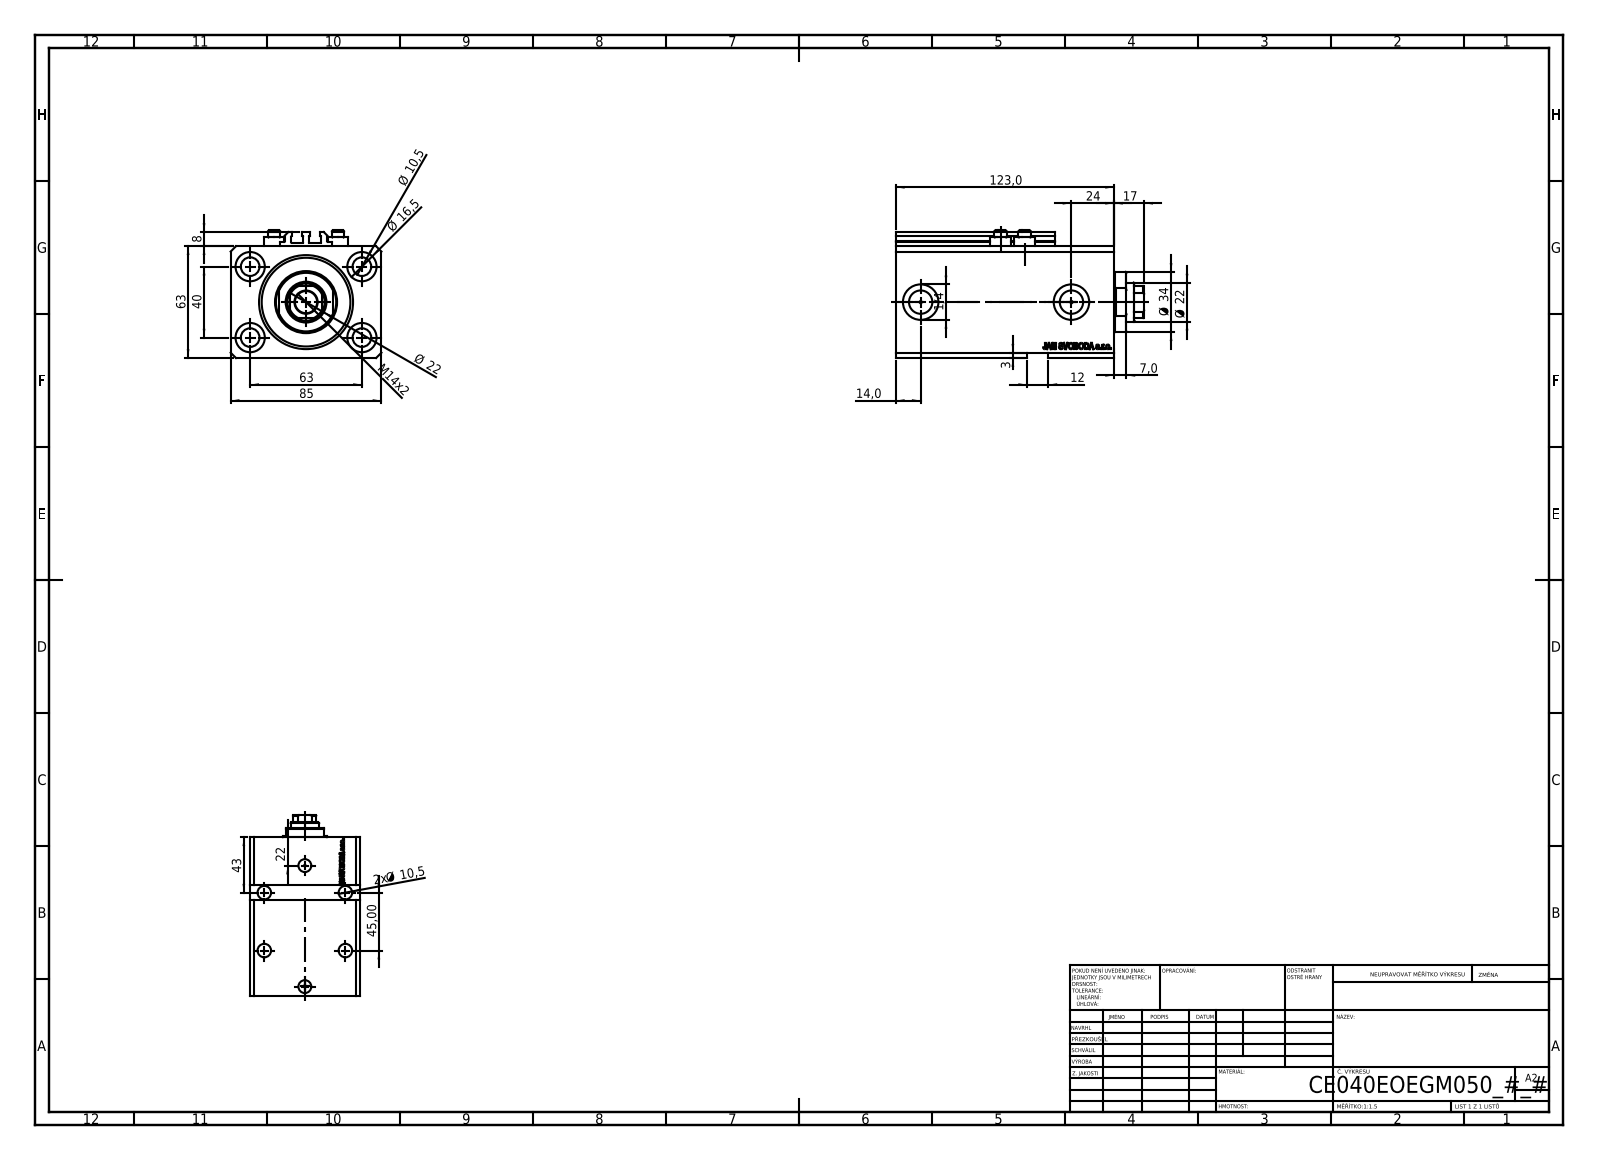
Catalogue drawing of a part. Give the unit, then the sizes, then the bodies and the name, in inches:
Units: inches
Overall size (bounding box): 5.512 × 3.346 × 2.835
Round holes (diameter × count): ⌀0.413 ×8, ⌀0.049 ×4, ⌀0.157 ×4, ⌀0.65 ×4, ⌀0.394 ×2, ⌀0.518 ×2, ⌀0.787 ×2, ⌀0.492 ×1, ⌀0.866 ×1, ⌀1.575 ×1, ⌀2.087 ×1
Round bosses / shafts (diameter × count): ⌀0.457 ×4, ⌀0.276 ×4, ⌀1.339 ×1
Partial cylindrical surfaces — rounded edges, fillets, slot ends (radius × count): R0.008 ×10, R0.413 ×1
Main face-to-face distances: 2.48, 3.346, 4.843, 0.669, 4.173, 0.449, 3.724, 4.394, 0.118, 2.205
Hole centre spacings: 1.469, 2.48, 0.535, 0.606, 0.983, 1.084, 1.324, 1.417
Volume: 33.97 in³ · Surface area: 185 in²
Bodies: 8 solids, 1107 faces (535 planar, 146 cylindrical, 426 other)
Part name (STEP PRODUCT): V250CE_E_Body; V250CE_C_VCP; V250CE_VC_E; ALLEN BOLT V250CE
STEP written by: SolidWorks 2019 (CONFIG_CONTROL_DESIGN)
